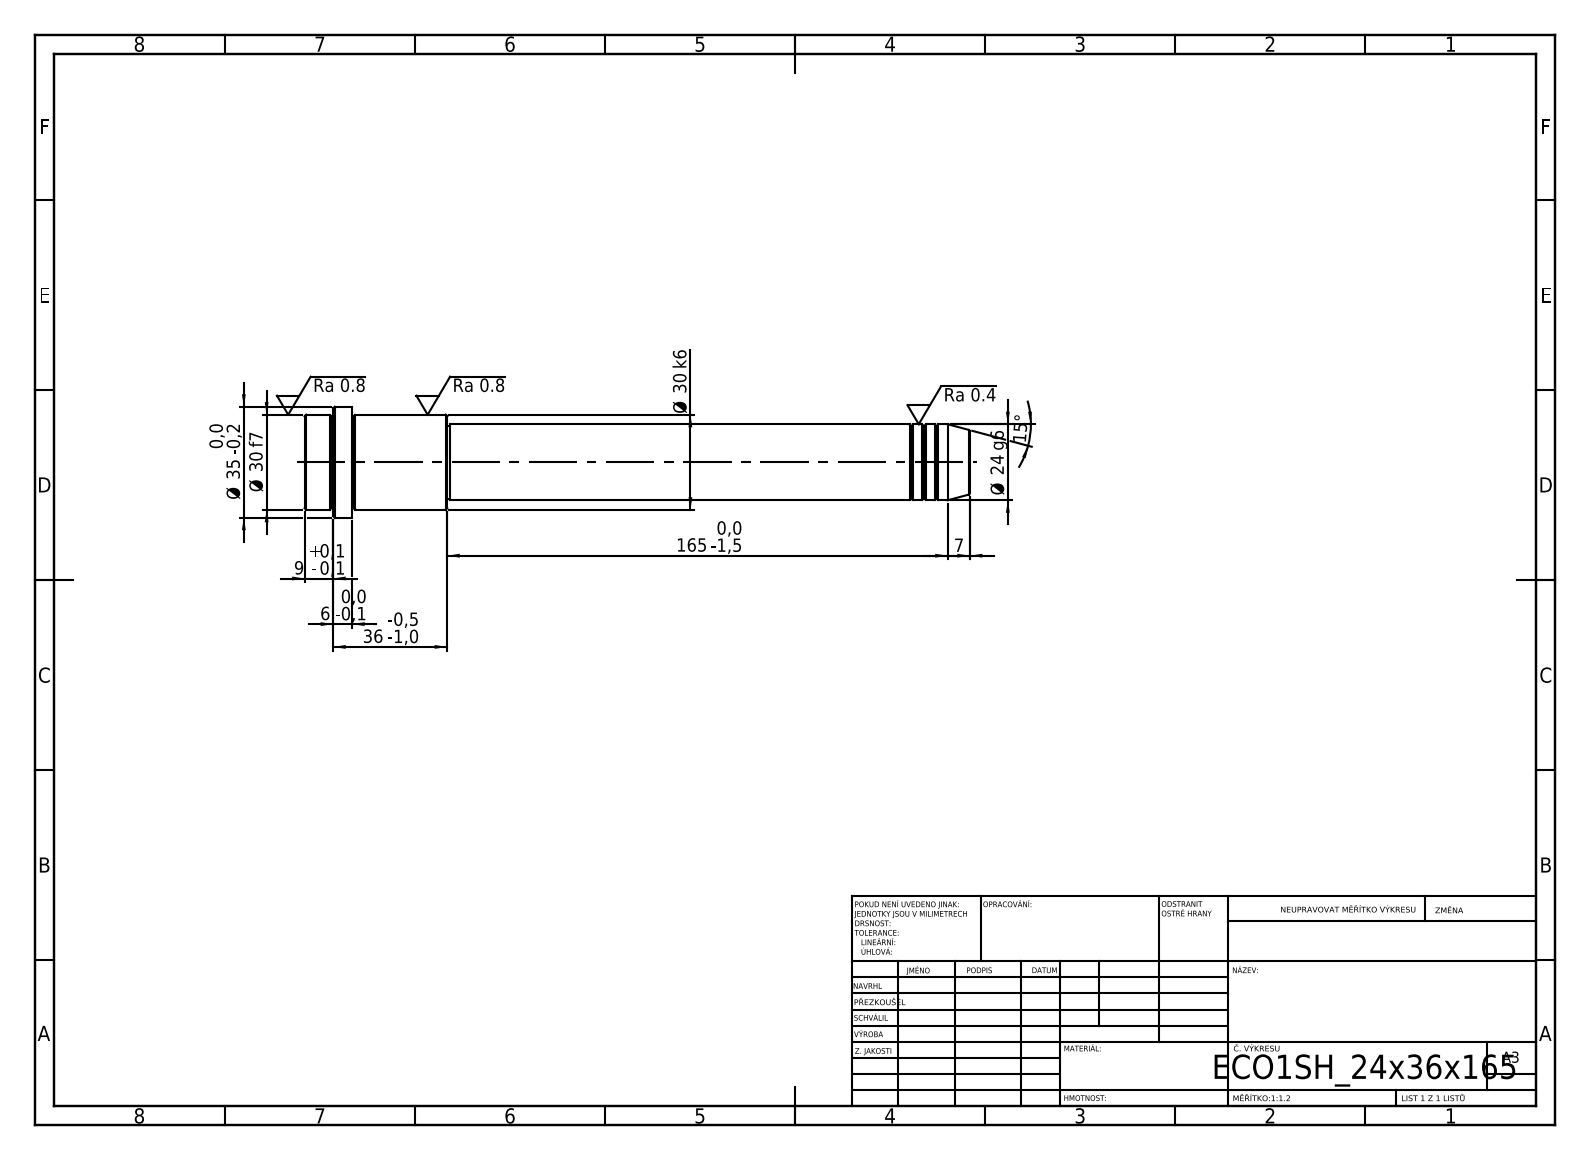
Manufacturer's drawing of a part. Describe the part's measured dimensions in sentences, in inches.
Its 3-D file was written by "SolidWorks 2019 (CONFIG_CONTROL_DESIGN)". It is 1 solid with 52 faces: 6 planar, 16 cylindrical and 30 other. Overall it measures 8.268 by 1.378 by 1.378 inches. Its volume is 6.547 cubic inches and its surface area 29.05 square inches. Round bosses or shafts: 1 of diameter 1.378, 1 of diameter 1.181, 1 of diameter 0.945, 1 of diameter 0.906. The main face-to-face distances are 8.268, 7.677, 0.591, 6.496, 1.181, 1.772, 7.913, 1.417, 0.236, 0.354.
